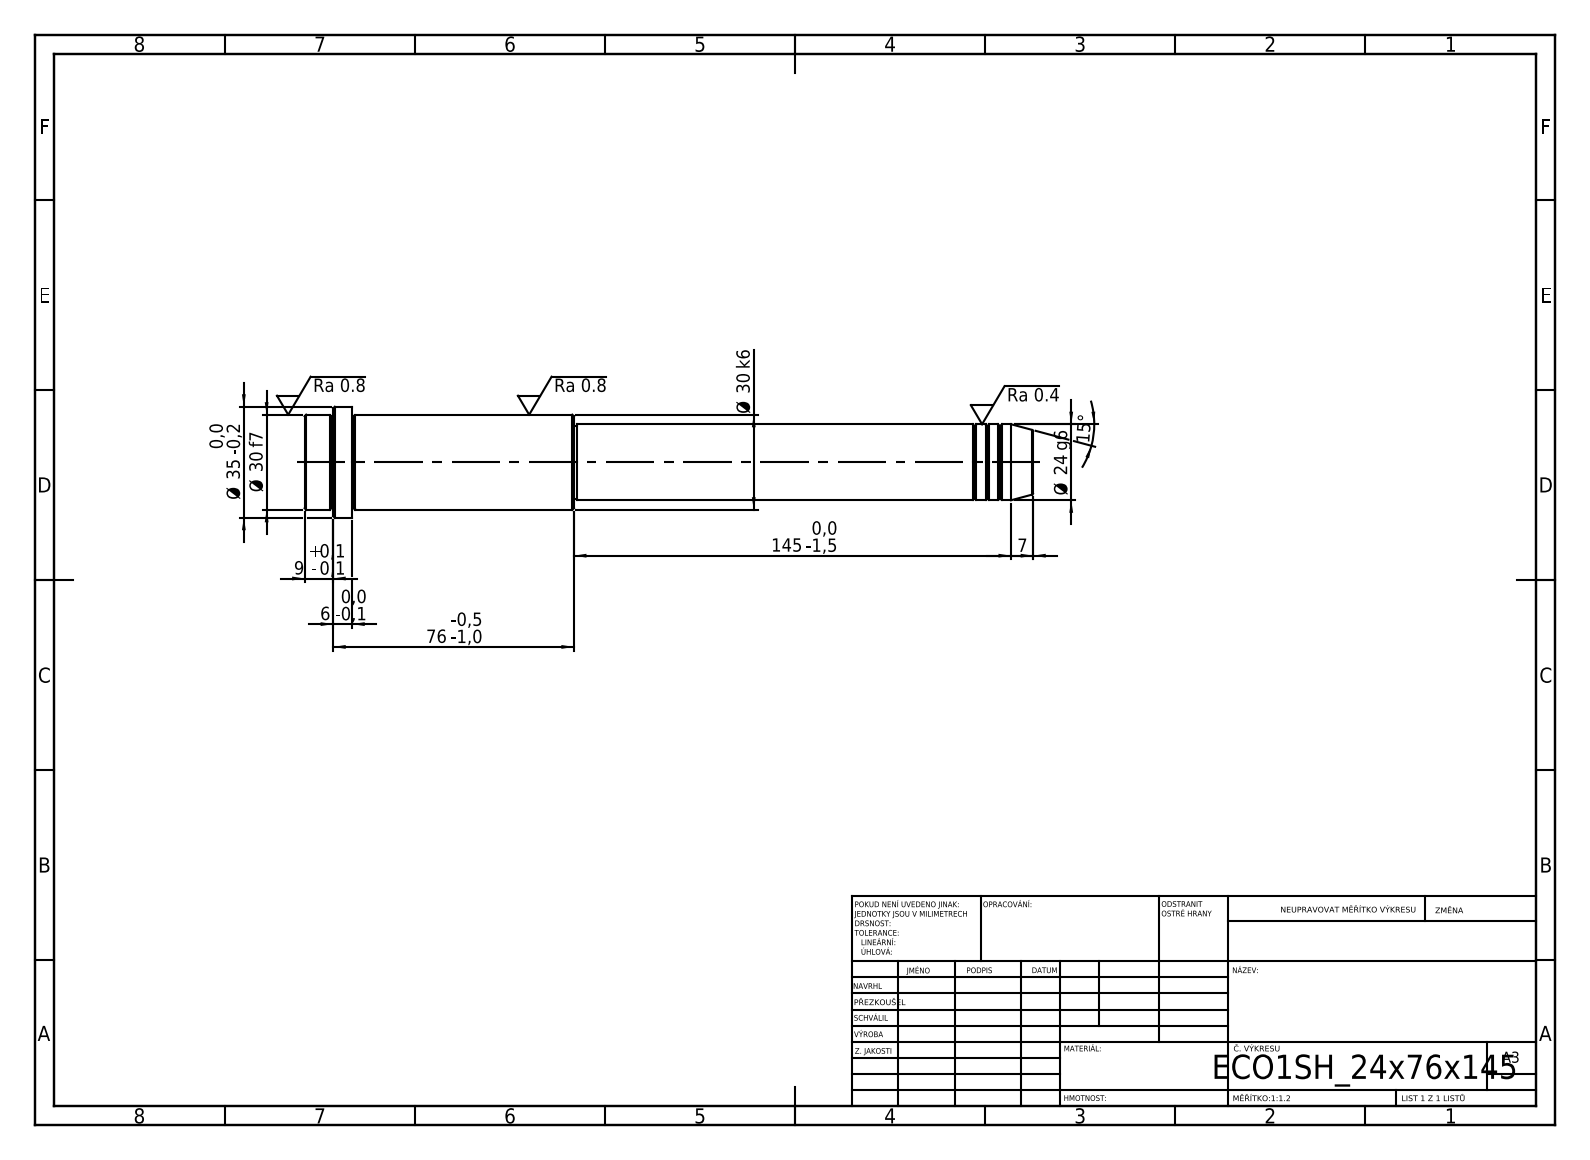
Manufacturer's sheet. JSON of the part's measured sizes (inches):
{"step_written_by": "SolidWorks 2019 (CONFIG_CONTROL_DESIGN)", "units": "inches", "bodies": {"solids": 1, "faces": 52, "planar": 6, "cylindrical": 16, "other": 30}, "overall_size": [9.055, 1.378, 1.378], "volume_in3": 7.72, "surface_area_in2": 32.56, "round_bosses_or_shafts": [[1.378, 1], [1.181, 1], [0.945, 1], [0.906, 1]], "face_to_face_distances": [9.055, 8.465, 0.591, 5.709, 2.756, 3.346, 8.701, 2.992, 0.236, 0.354]}
